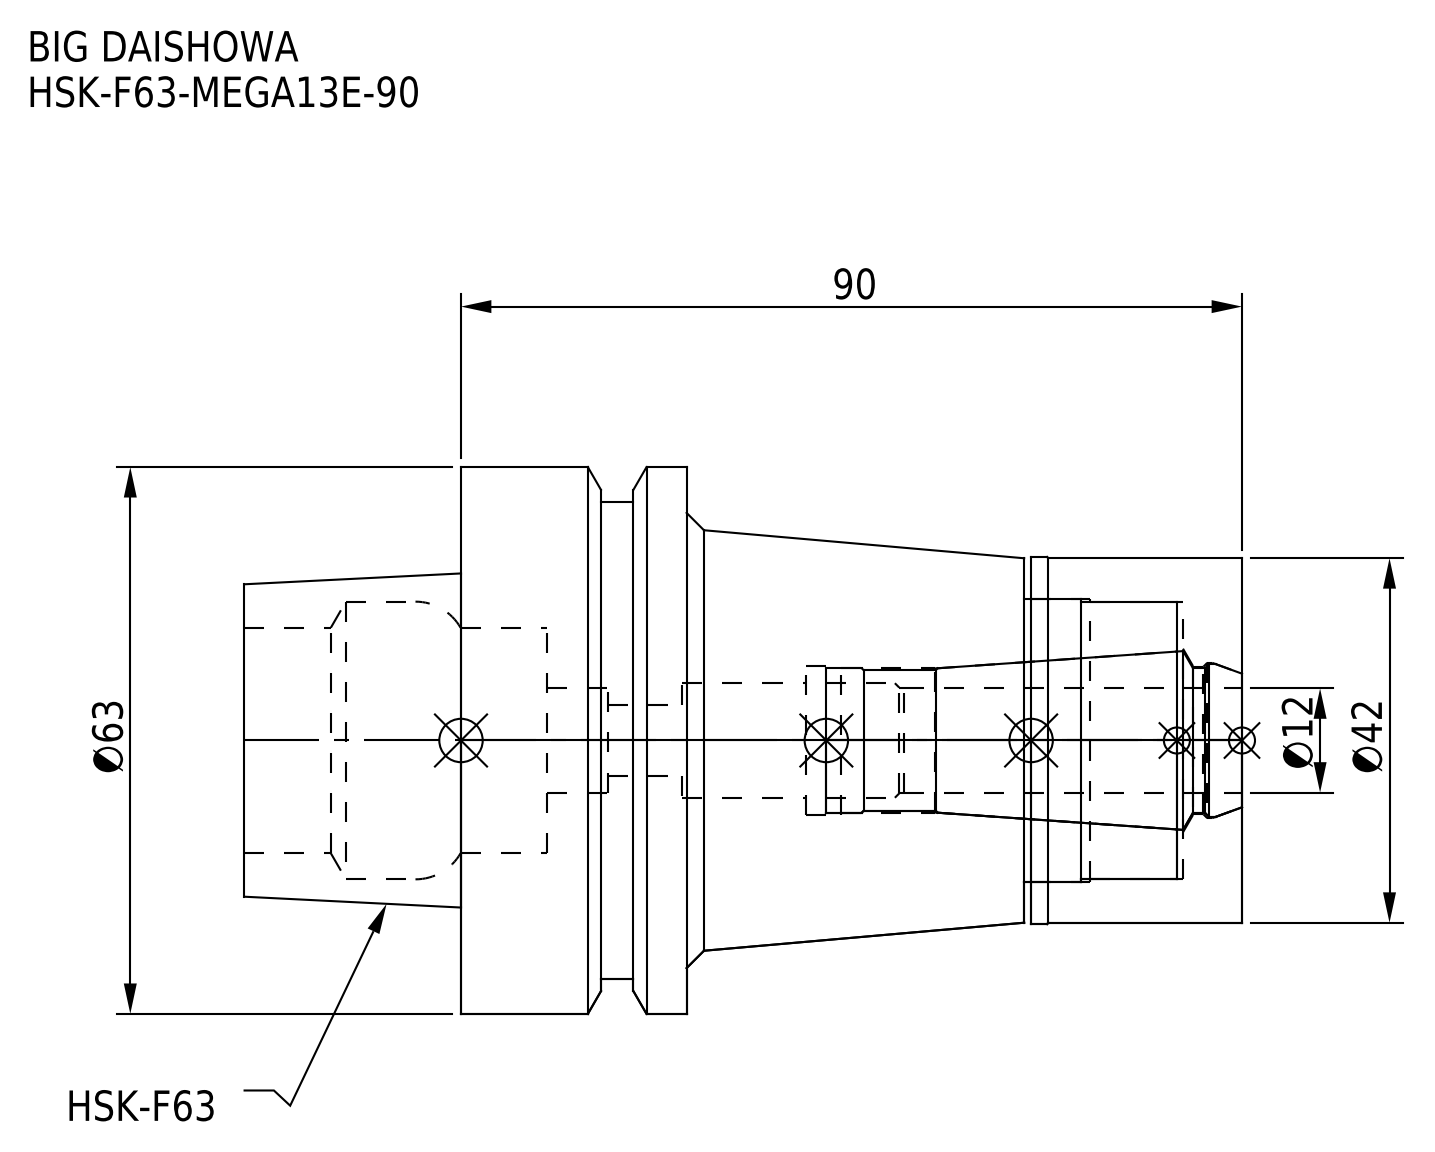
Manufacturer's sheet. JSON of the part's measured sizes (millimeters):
{"part_name": "HSK-F63-MEGA13E-90; DXF_TEMP_ASSY_ASM_4_ASM.stp; HF63ME13090-120_ASM.stp; HSK-F63-MEGA13E-90-120.stp (+3 more)", "step_written_by": "SolidWorks 2019 (CONFIG_CONTROL_DESIGN)", "units": "millimeters", "bodies": {"solids": 2, "faces": 81, "planar": 17, "cylindrical": 40, "other": 24}, "overall_size": [115, 63, 63], "volume_mm3": 164298, "surface_area_mm2": 36178, "round_holes": [[8.25, 1], [12, 1], [13.3, 1], [16.6, 1], [17, 1], [17.2, 1], [17.9, 1], [26, 1], [32, 1], [32.5, 1]], "round_bosses_or_shafts": [[63, 1], [55, 1], [42.3, 1], [42, 1]], "face_to_face_distances": [90, 64, 26, 25.1, 24.3, 39.7, 65.7, 0.8, 38.9, 64.9]}
